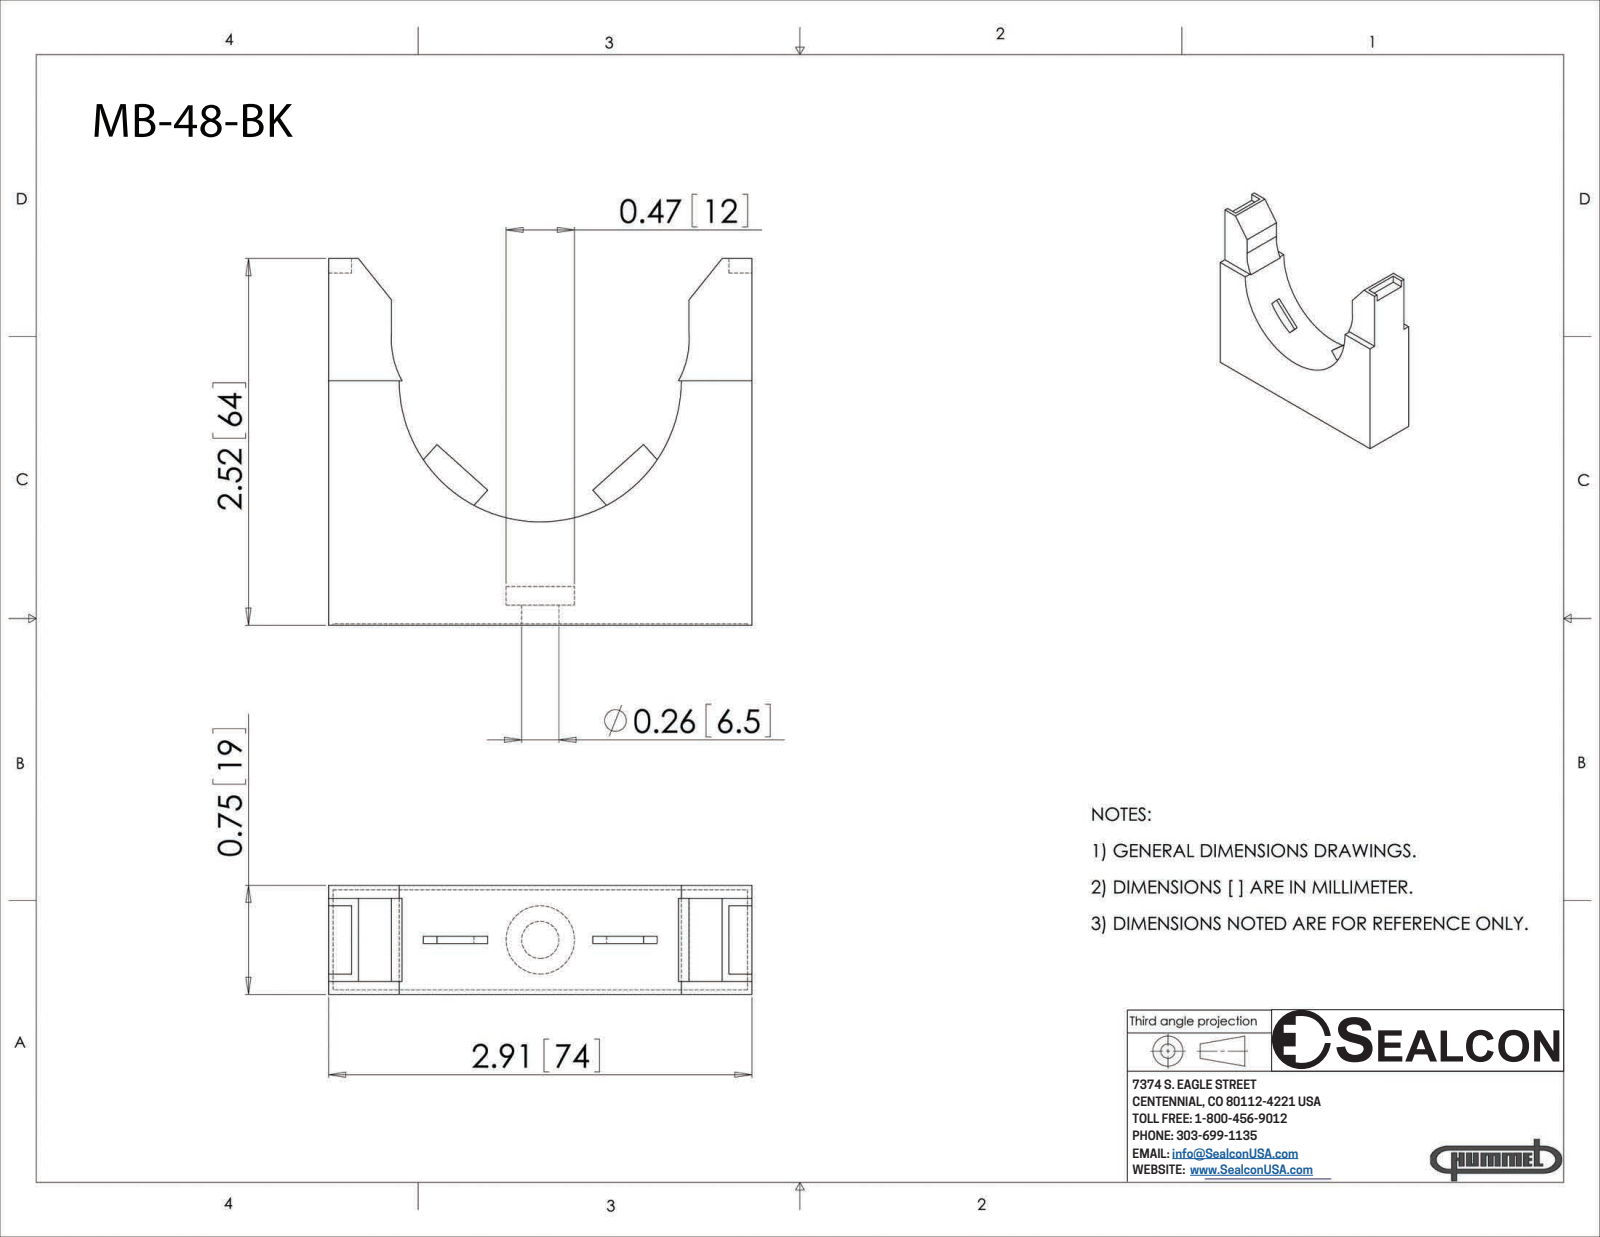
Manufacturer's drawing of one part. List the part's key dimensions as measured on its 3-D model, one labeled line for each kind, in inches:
Part name (STEP PRODUCT): MB-48-BK
STEP written by: SolidWorks 2008 (CONFIG_CONTROL_DESIGN)
Units: inches
Bodies: 1 solid, 54 faces (46 planar, 8 cylindrical, 0 other)
Overall size (bounding box): 2.91 × 2.52 × 0.75
Volume: 2.887 in³ · Surface area: 18.61 in²
Round holes (diameter × count): ⌀0.256 ×1, ⌀0.47 ×1
Partial cylindrical surfaces — rounded edges, fillets, slot ends (radius × count): R0.6 ×2, R0.97 ×1
Main face-to-face distances: 0.75, 2.91, 0.089, 0.661, 0.571, 0.35, 0.4, 0.261, 0.311, 0.433
